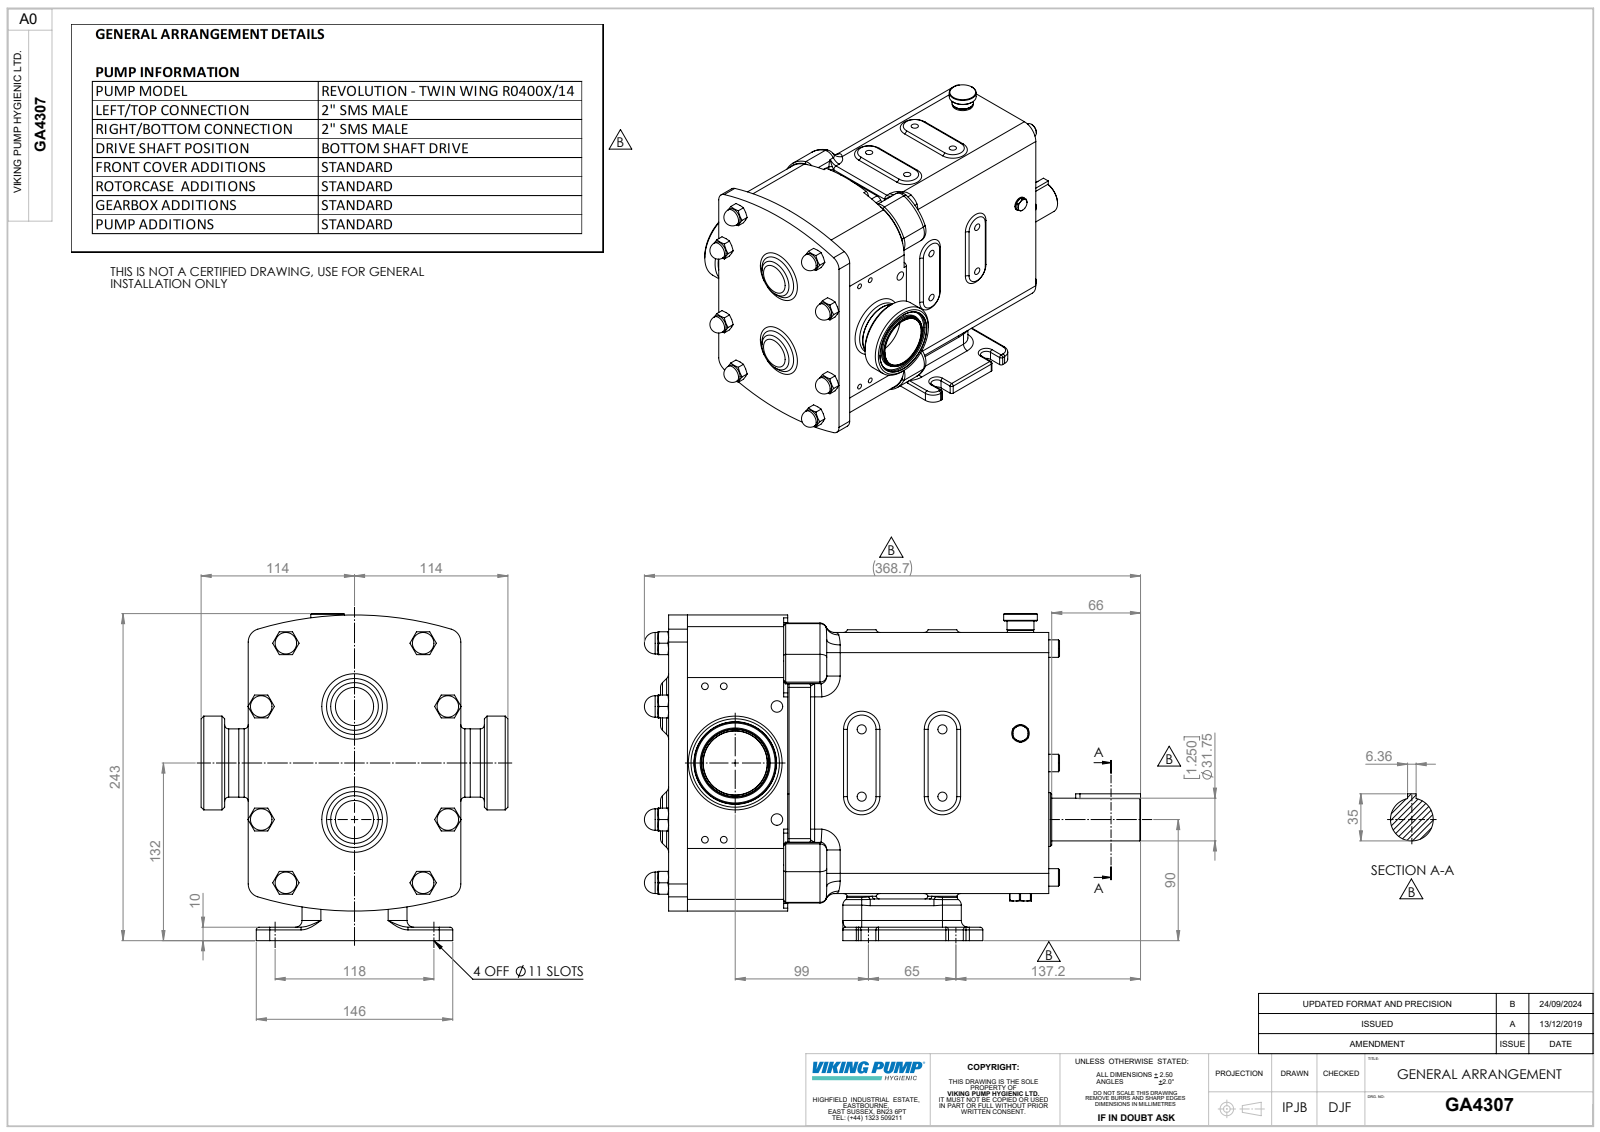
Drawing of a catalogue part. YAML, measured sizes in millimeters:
part_name: "Copy of Z94-5101-33 - 2 INCH SMS681^GA4307; Copy of R0400 CPP H BSD^GA4307; GA4307"
step_written_by: "SolidWorks 2023 (AUTOMOTIVE_DESIGN)"
units: millimeters
bodies: {solids: 3, faces: 968, planar: 296, cylindrical: 305, other: 367}
overall_size: [368.7, 243, 228]
volume: 7390000
surface_area: 384764
round_holes:
  - {diameter: 6.8, count: 8}
  - {diameter: 5, count: 4}
  - {diameter: 8.6, count: 2}
  - {diameter: 23, count: 1}
  - {diameter: 47.6, count: 1}
  - {diameter: 61, count: 1}
round_bosses_or_shafts:
  - {diameter: 16, count: 8}
  - {diameter: 13, count: 7}
  - {diameter: 69.7, count: 1}
  - {diameter: 50.85, count: 1}
  - {diameter: 50.7, count: 1}
  - {diameter: 50.5, count: 1}
  - {diameter: 40, count: 1}
  - {diameter: 38, count: 1}
partial_cylinders:
  - {radius: 10, count: 30}
  - {radius: 3, count: 28}
  - {radius: 2, count: 24}
  - {radius: 5, count: 19}
  - {radius: 5.9, count: 8}
  - {radius: 15, count: 8}
  - {radius: 5.5, count: 4}
  - {radius: 8, count: 4}
face_to_face_distances: [194, 24, 88.5, 110, 282.5, 134, 193, 89.5, 1, 22]
hole_center_spacings: [50, 60, 78.1, 14, 42.25, 52.2, 55.56, 57.63]
